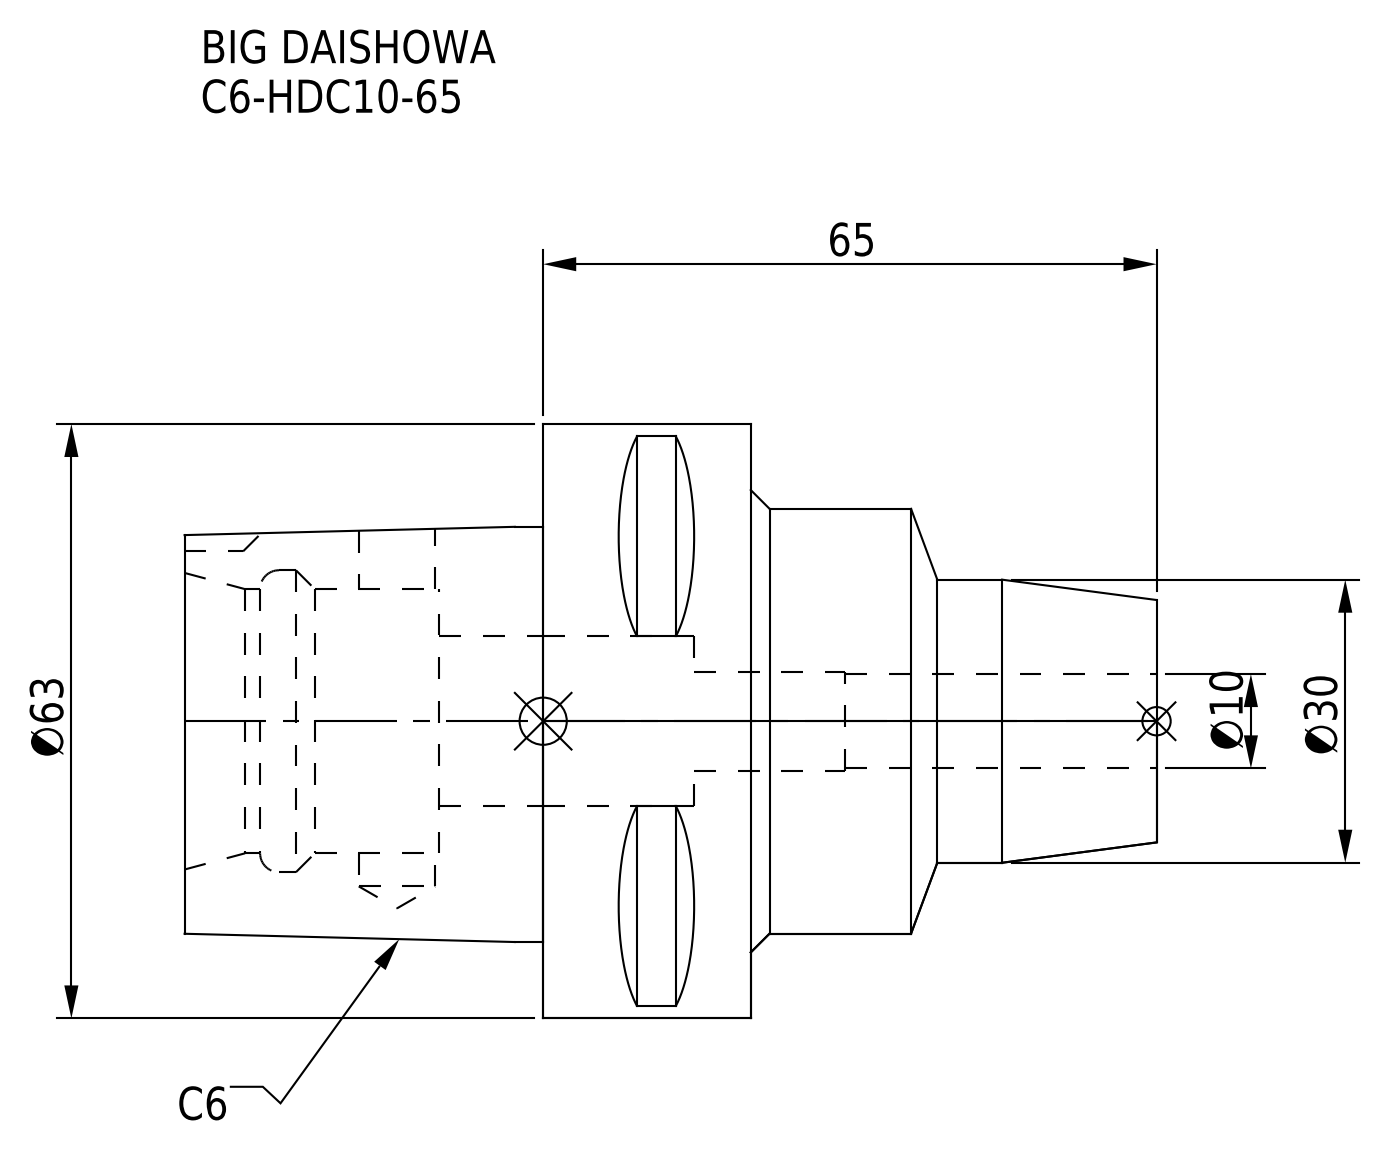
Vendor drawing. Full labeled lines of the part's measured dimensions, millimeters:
Part name (STEP PRODUCT): C6-HDC10-65
STEP written by: CREO PARAMETRIC BY PTC INC, 2016380 (AUTOMOTIVE_DESIGN)
Units: millimetres
Bodies: 1 solid, 68 faces (29 planar, 23 cylindrical, 16 other)
Overall size (bounding box): 103 × 63 × 63
Volume: 137 867 mm³ · Surface area: 25 760 mm²
Round holes (diameter × count): ⌀8.1 ×1, ⌀10 ×1, ⌀10.5 ×1, ⌀18 ×1, ⌀28 ×1, ⌀32 ×1
Round bosses / shafts (diameter × count): ⌀63 ×1, ⌀45 ×1, ⌀30 ×1
Partial cylindrical surfaces — rounded edges, fillets, slot ends (radius × count): R5 ×1
Main face-to-face distances: 22, 27, 60, 38, 43, 65, 103, 33, 76, 11
